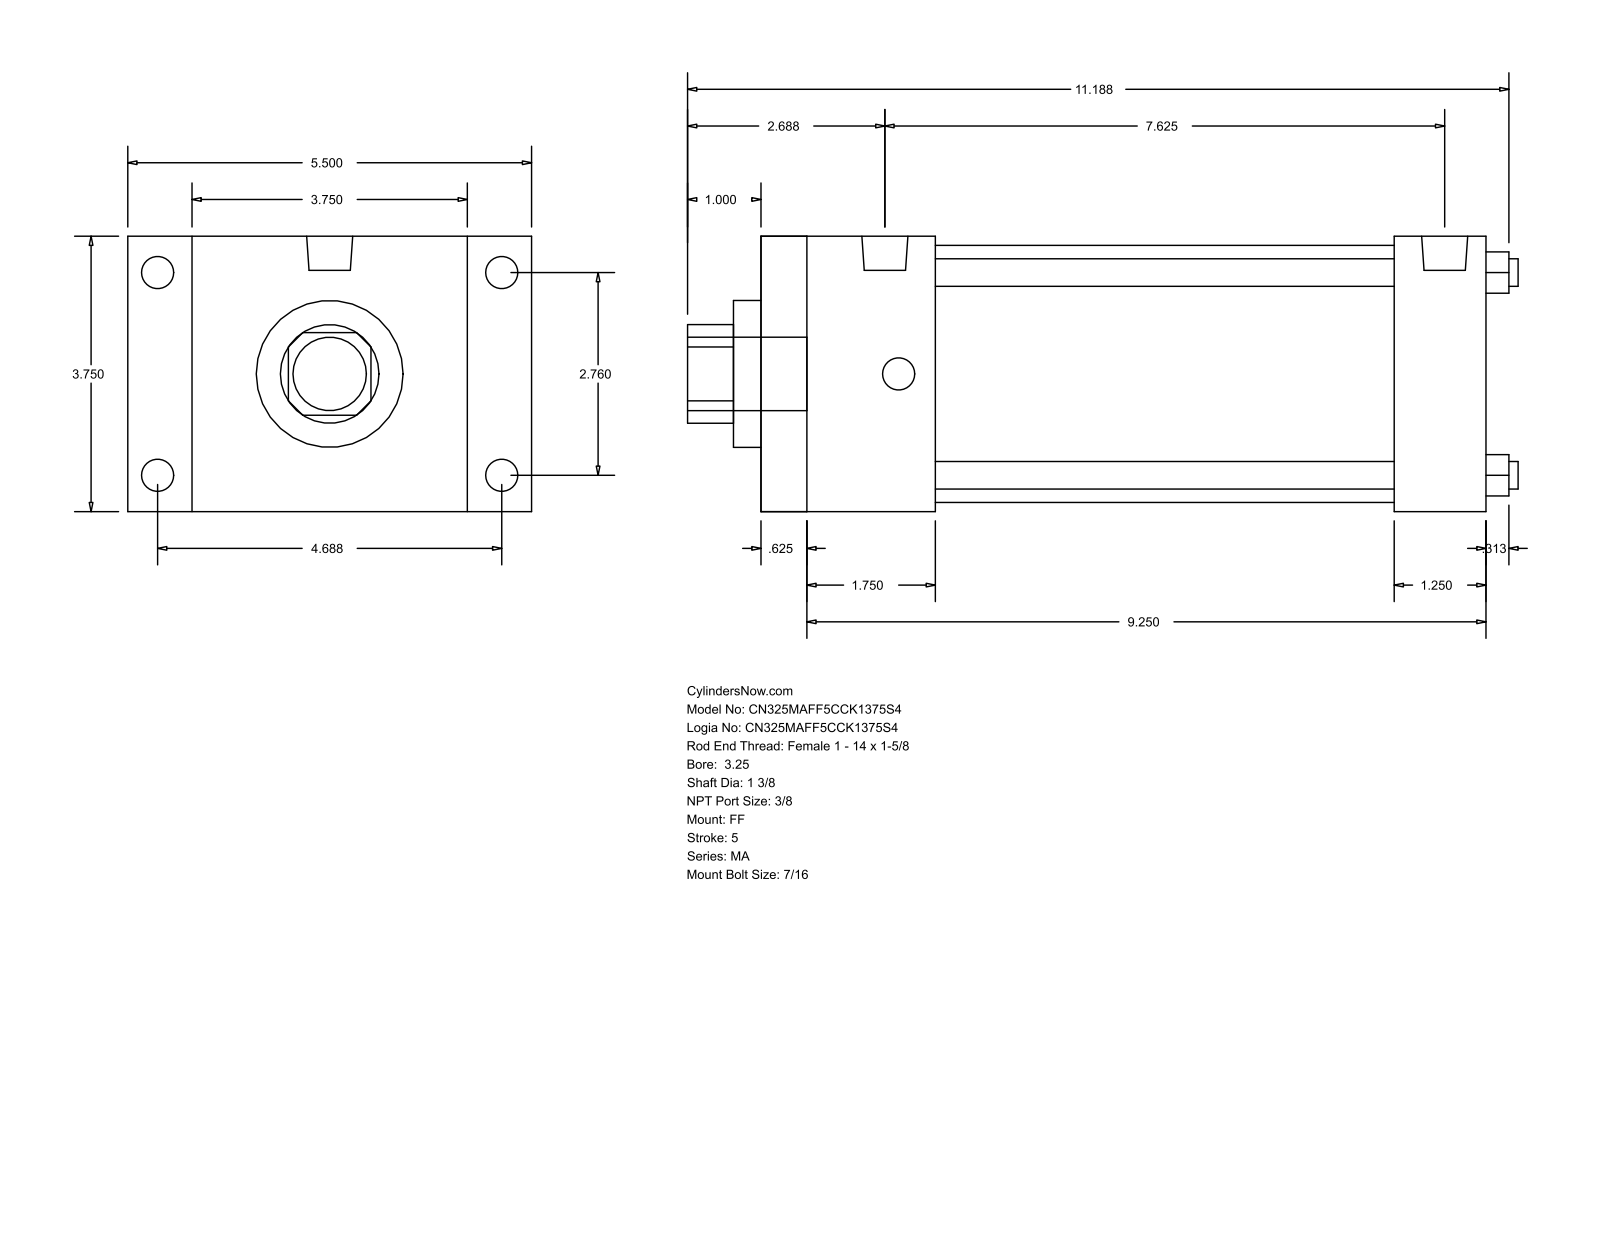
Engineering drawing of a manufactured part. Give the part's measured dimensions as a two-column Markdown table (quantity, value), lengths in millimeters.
| quantity | value |
| --- | --- |
| part name | MA_FF__0325_1.375 |
| STEP written by | GSSL Pune (CONFIG_CONTROL_DESIGN) |
| units | millimeters |
| bodies | 0 solids, 92 faces (64 planar, 28 cylindrical, 0 other) |
| overall size | 287.34 × 139.7 × 95.25 |
| round holes (diameter × count) | 9.53 × 4, 34.92 × 1, 50.8 × 1, 88.9 × 1 |
| round bosses / shafts (diameter × count) | 11.11 × 8, 15.93 × 2, 25.4 × 1 |
| partial cylindrical surfaces (radius × count) | 17.06 × 1 |
| main face-to-face distances | 95.24, 250.83, 15.87, 234.96, 22.23, 117.47, 60.32, 219.07, 44.45, 203.2 |
| hole center spacings | 49.57, 70.1, 99.14 |
